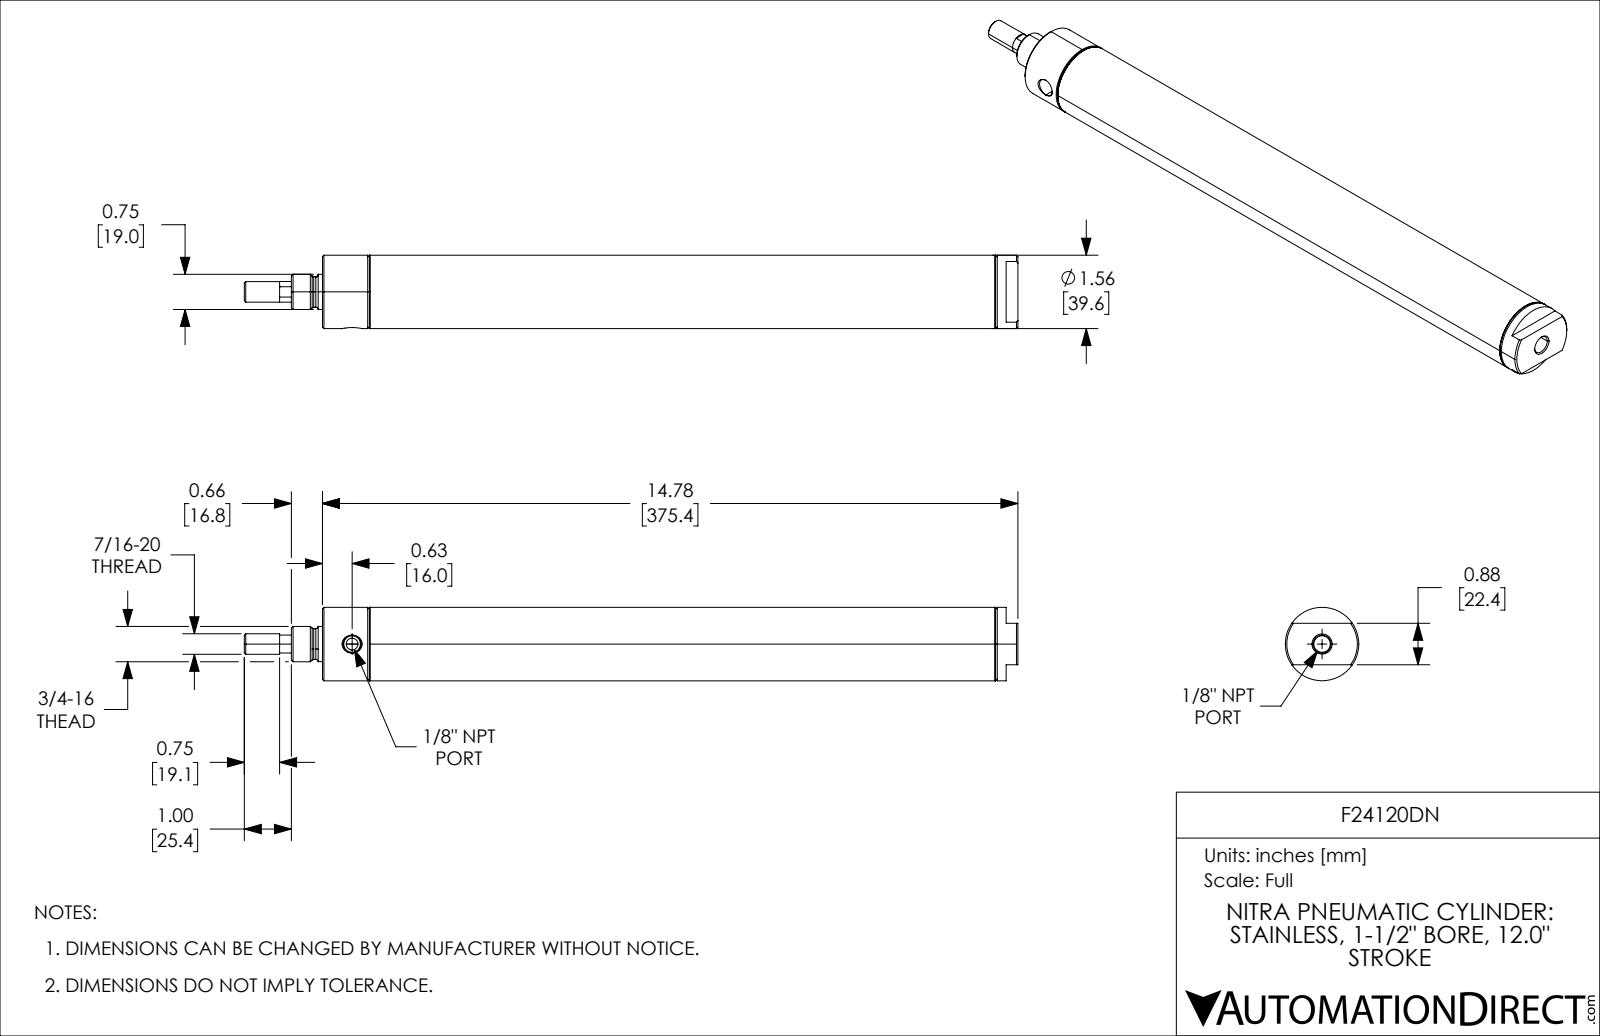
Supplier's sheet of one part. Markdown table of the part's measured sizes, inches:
| quantity | value |
| --- | --- |
| part name | F24120DN; F24120DN_3; F24120DN_7; F24120DN_5 (+1 more) |
| STEP written by | SolidWorks 2021 (CONFIG_CONTROL_DESIGN) |
| units | inches |
| bodies | 4 solids, 126 faces (28 planar, 42 cylindrical, 56 other) |
| overall size | 16.438 × 1.56 × 1.56 |
| volume | 8.459 in³ |
| surface area | 181.1 in² |
| round holes (diameter × count) | 0.25 × 1, 0.462 × 1, 0.973 × 1, 1.431 × 1 |
| round bosses / shafts (diameter × count) | 1.56 × 1, 1.511 × 1, 0.75 × 1, 0.748 × 1, 0.654 × 1, 0.438 × 1, 0.437 × 1 |
| main face-to-face distances | 0.875, 0.25, 0.438, 12, 12.875, 1.215, 13.215, 14.09, 14.778, 13.563 |
